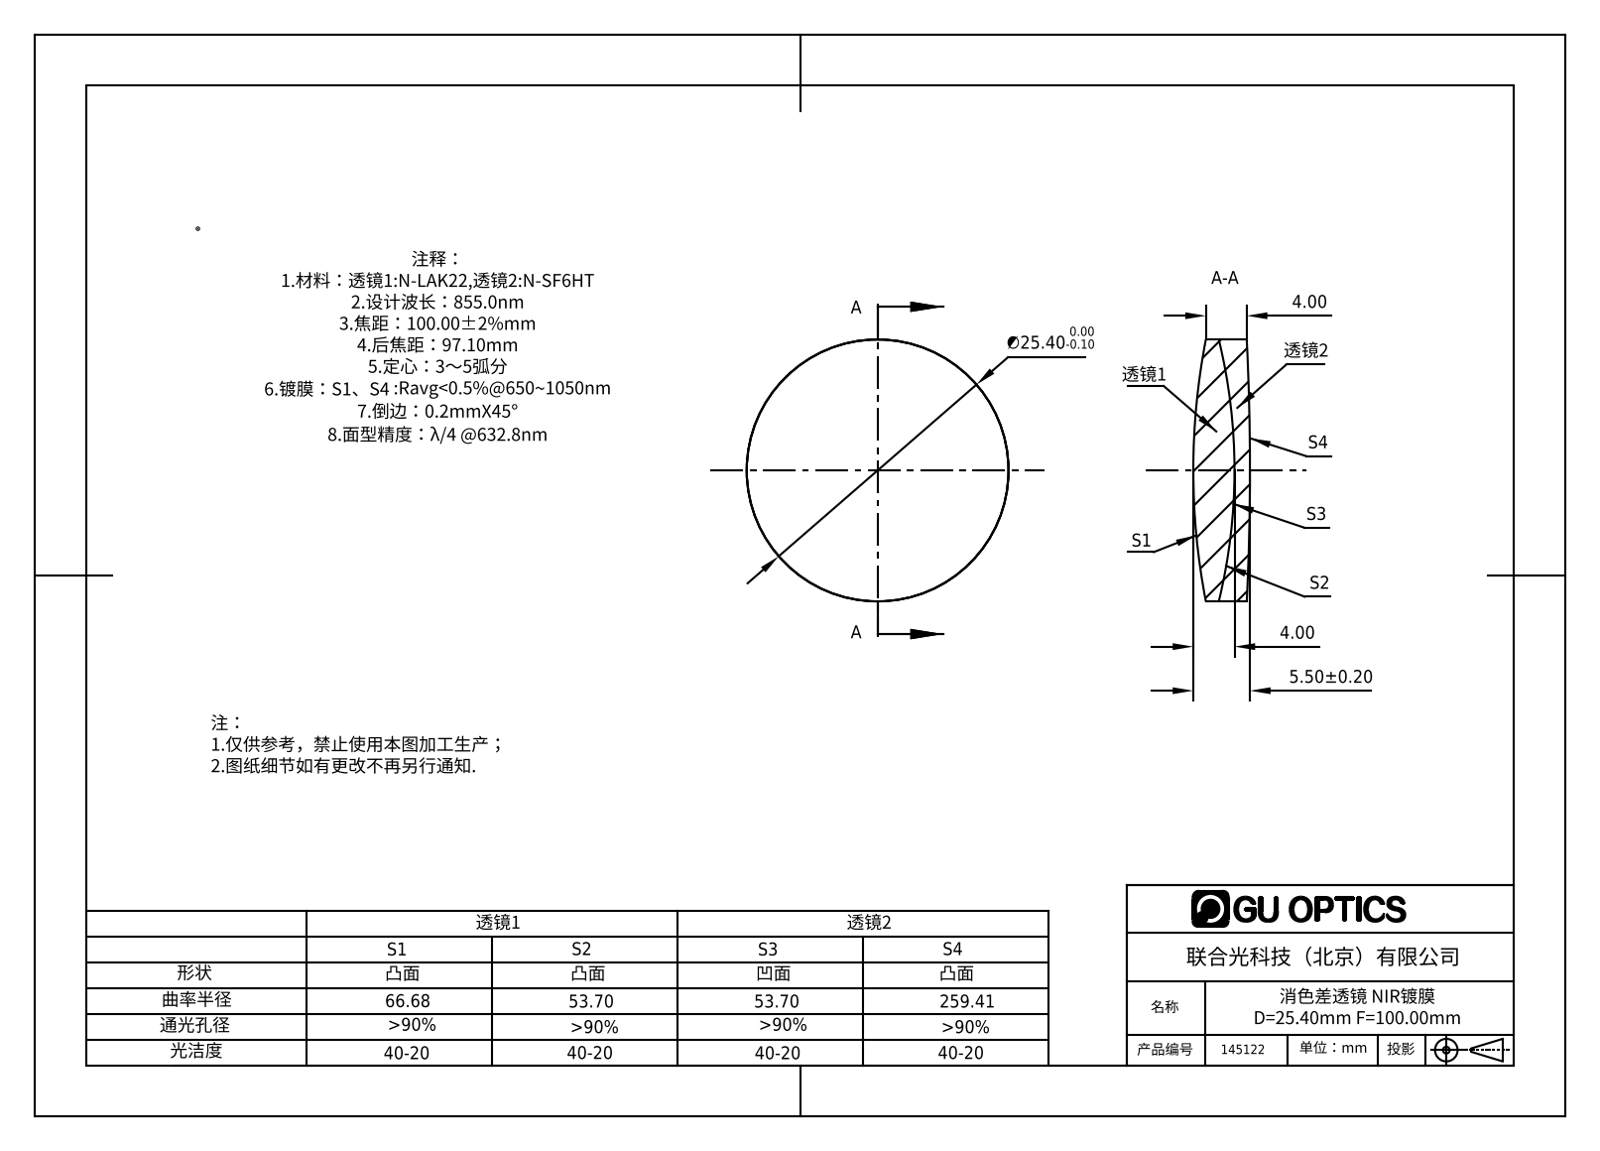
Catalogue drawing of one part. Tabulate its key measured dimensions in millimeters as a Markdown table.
| quantity | value |
| --- | --- |
| part name | 145122 |
| STEP written by | SolidWorks 2016 (AUTOMOTIVE_DESIGN) |
| units | millimeters |
| bodies | 2 solids, 12 faces (0 planar, 4 cylindrical, 8 other) |
| overall size | 25.4 × 25.4 × 5.5 |
| volume | 2 400 mm³ |
| surface area | 2 363 mm² |
| round bosses / shafts (diameter × count) | 25.4 × 1 |
